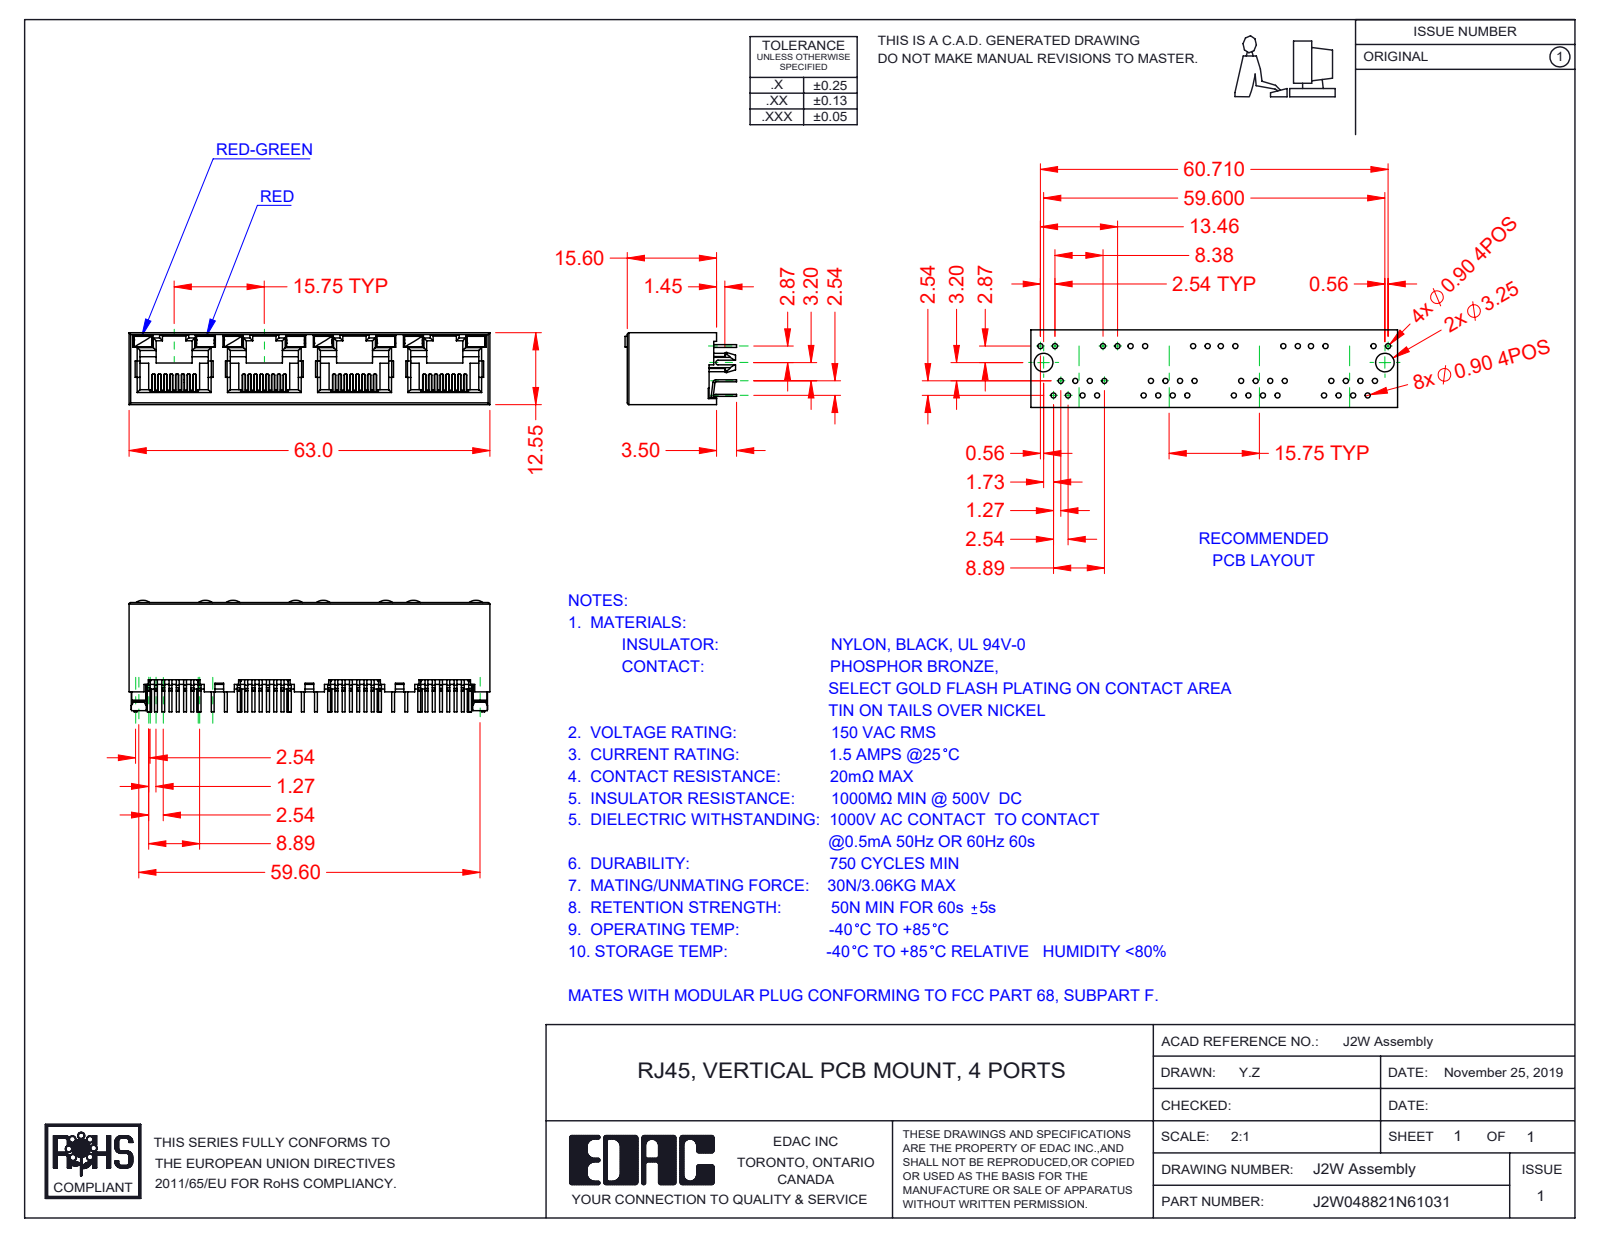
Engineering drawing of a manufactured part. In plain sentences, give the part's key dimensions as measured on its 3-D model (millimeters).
The part is named "2W LED RH_2-Red; 2W Contact Lock; J2W048821N62131; 2W Insulator (+2 more)". Its 3-D file was written by "SolidWorks 2016 (CONFIG_CONTROL_DESIGN)". It is 45 solids with 3139 faces: 2600 planar, 481 cylindrical and 58 other. Overall it measures 63 by 19.5 by 12.55 millimeters. Its volume is 5 335 cubic millimeters and its surface area 13 144 square millimeters. Partial cylindrical surfaces (rounded edges, fillets, slot ends): 64 of radius 0.15, 29 of radius 0.2, 28 of radius 0.5, 14 of radius 0.3, 8 of radius 0.45, 8 of radius 2, 2 of radius 0.25, 2 of radius 1.5. The main face-to-face distances are 12.55, 11.9, 0.65, 15.75, 0.36, 1.5, 0.78, 0.6, 11.3, 31.5.
